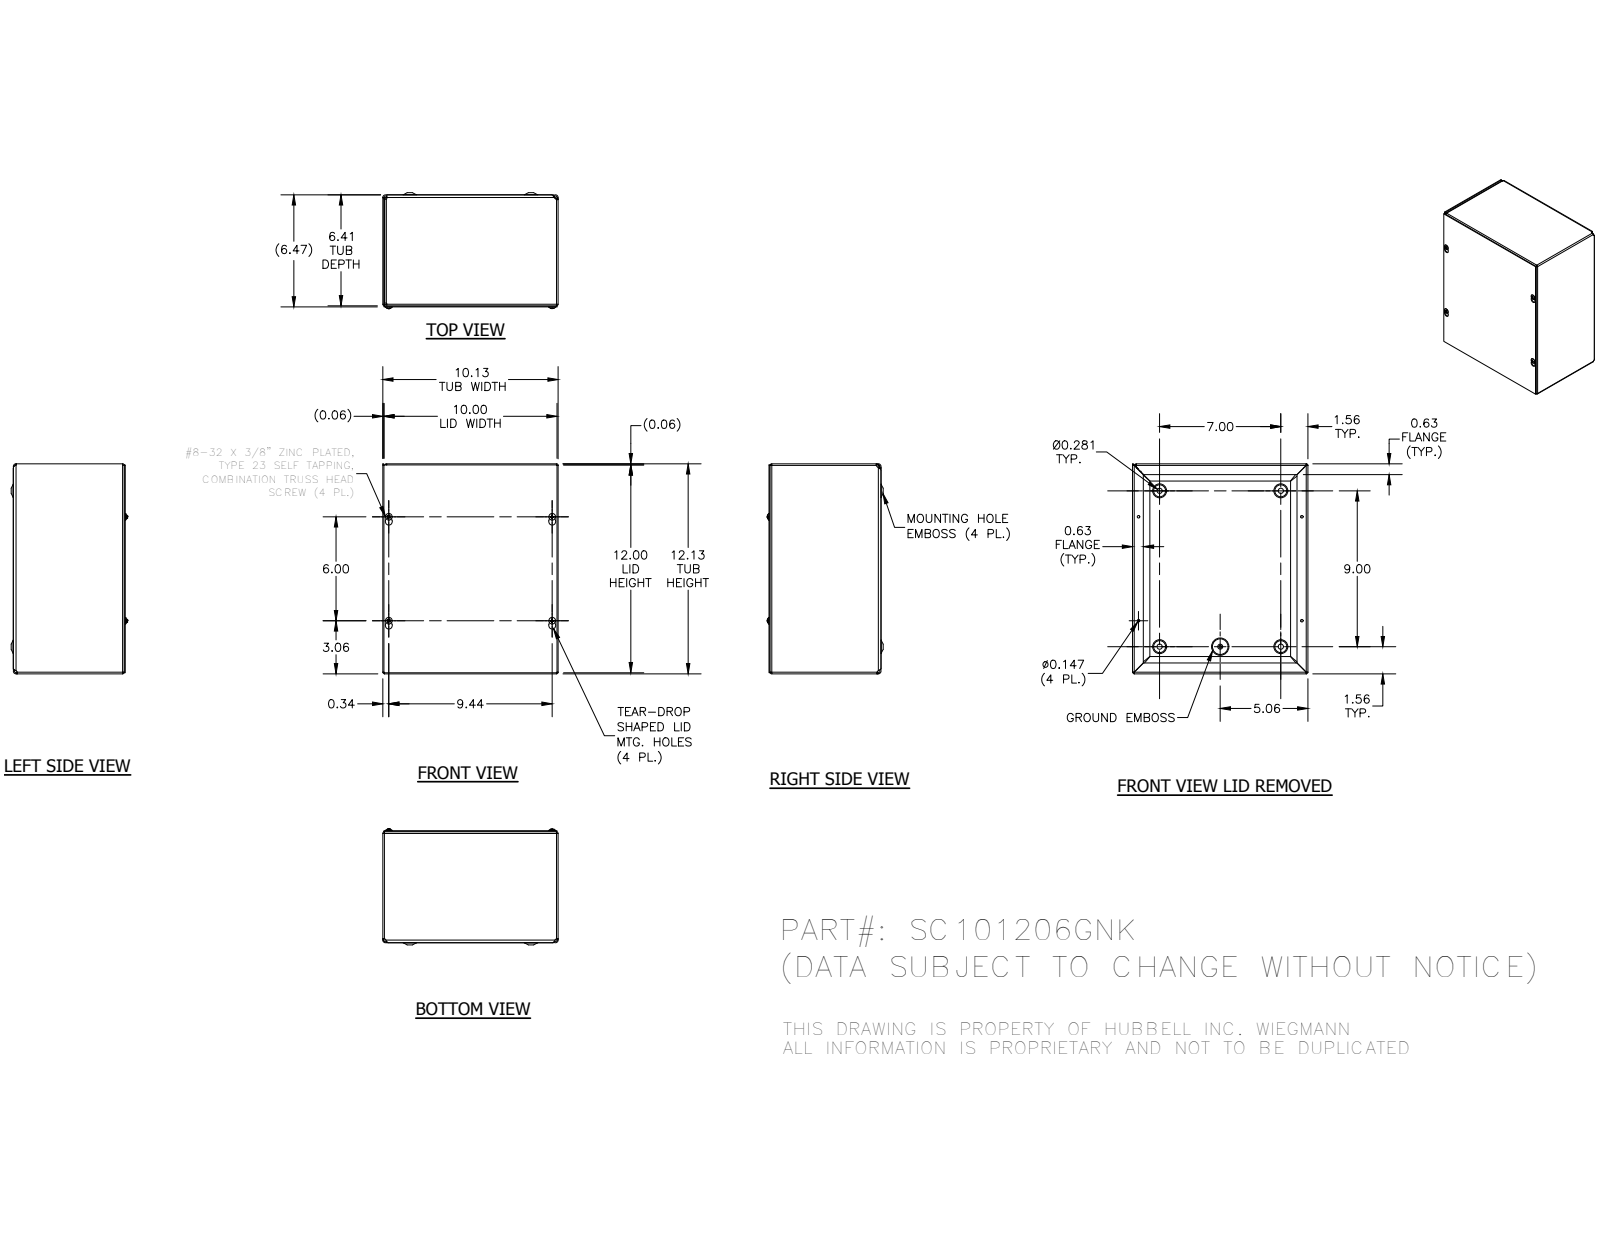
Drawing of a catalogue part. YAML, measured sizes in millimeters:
part_name: "SC1012GNKBKP; SC101206GNKWRA; SC1012GNKLID; 34056 (+1 more)"
step_written_by: "Autodesk Inventor 2014 (AUTOMOTIVE_DESIGN)"
units: millimeters
bodies: {solids: 7, faces: 358, planar: 133, cylindrical: 73, other: 152}
overall_size: [307.98, 257.18, 170]
volume: 586121
surface_area: 752033
round_holes:
  - {diameter: 3.73, count: 4}
  - {diameter: 7.62, count: 4}
  - {diameter: 4.19, count: 1}
round_bosses_or_shafts:
  - {diameter: 9.75, count: 4}
  - {diameter: 4.17, count: 4}
  - {diameter: 5.8, count: 1}
partial_cylinders:
  - {radius: 0.79, count: 8}
  - {radius: 2.37, count: 8}
  - {radius: 1.4, count: 4}
  - {radius: 1.57, count: 4}
  - {radius: 2.38, count: 4}
  - {radius: 2.97, count: 4}
  - {radius: 3.15, count: 4}
  - {radius: 3.17, count: 4}
face_to_face_distances: [1.57, 161.12, 255.6, 306.4, 162.69, 1.59, 162.71, 164.28, 254.03, 257.17]
hole_center_spacings: [88.9, 152.4, 177.8, 192.98, 193.02, 212.2, 225.05, 228.6]
